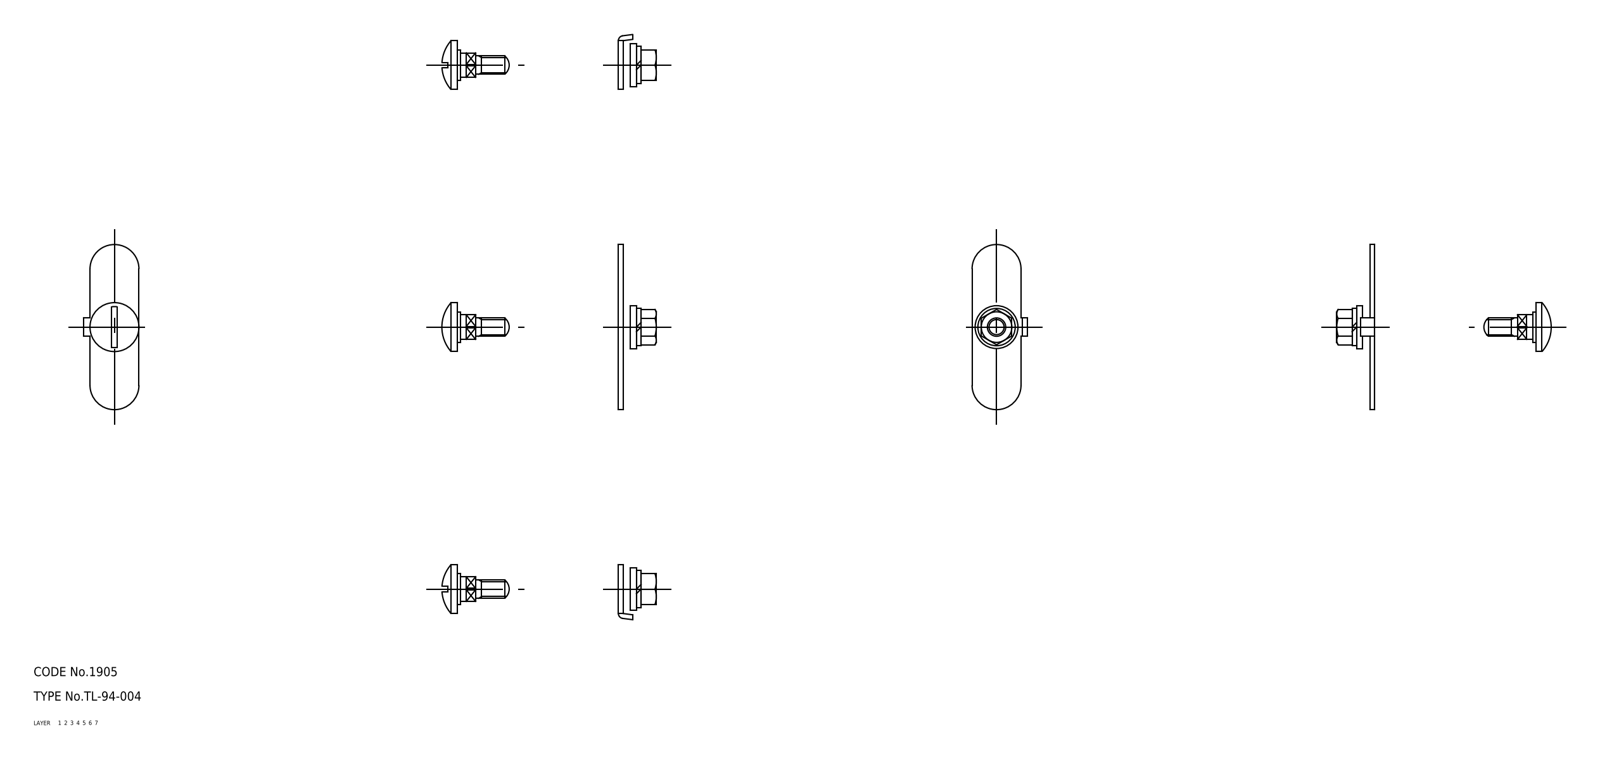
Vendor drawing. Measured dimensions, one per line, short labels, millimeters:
name: washer; nut; knob; base (+1 more)
written by: CADfix (AUTOMOTIVE_DESIGN)
unit: mm
bodies: 4 solids, 68 faces (0 planar, 0 cylindrical, 68 other)
size: 54 × 21.97 × 18
volume: 3 168 mm³; area: 3 634 mm²
